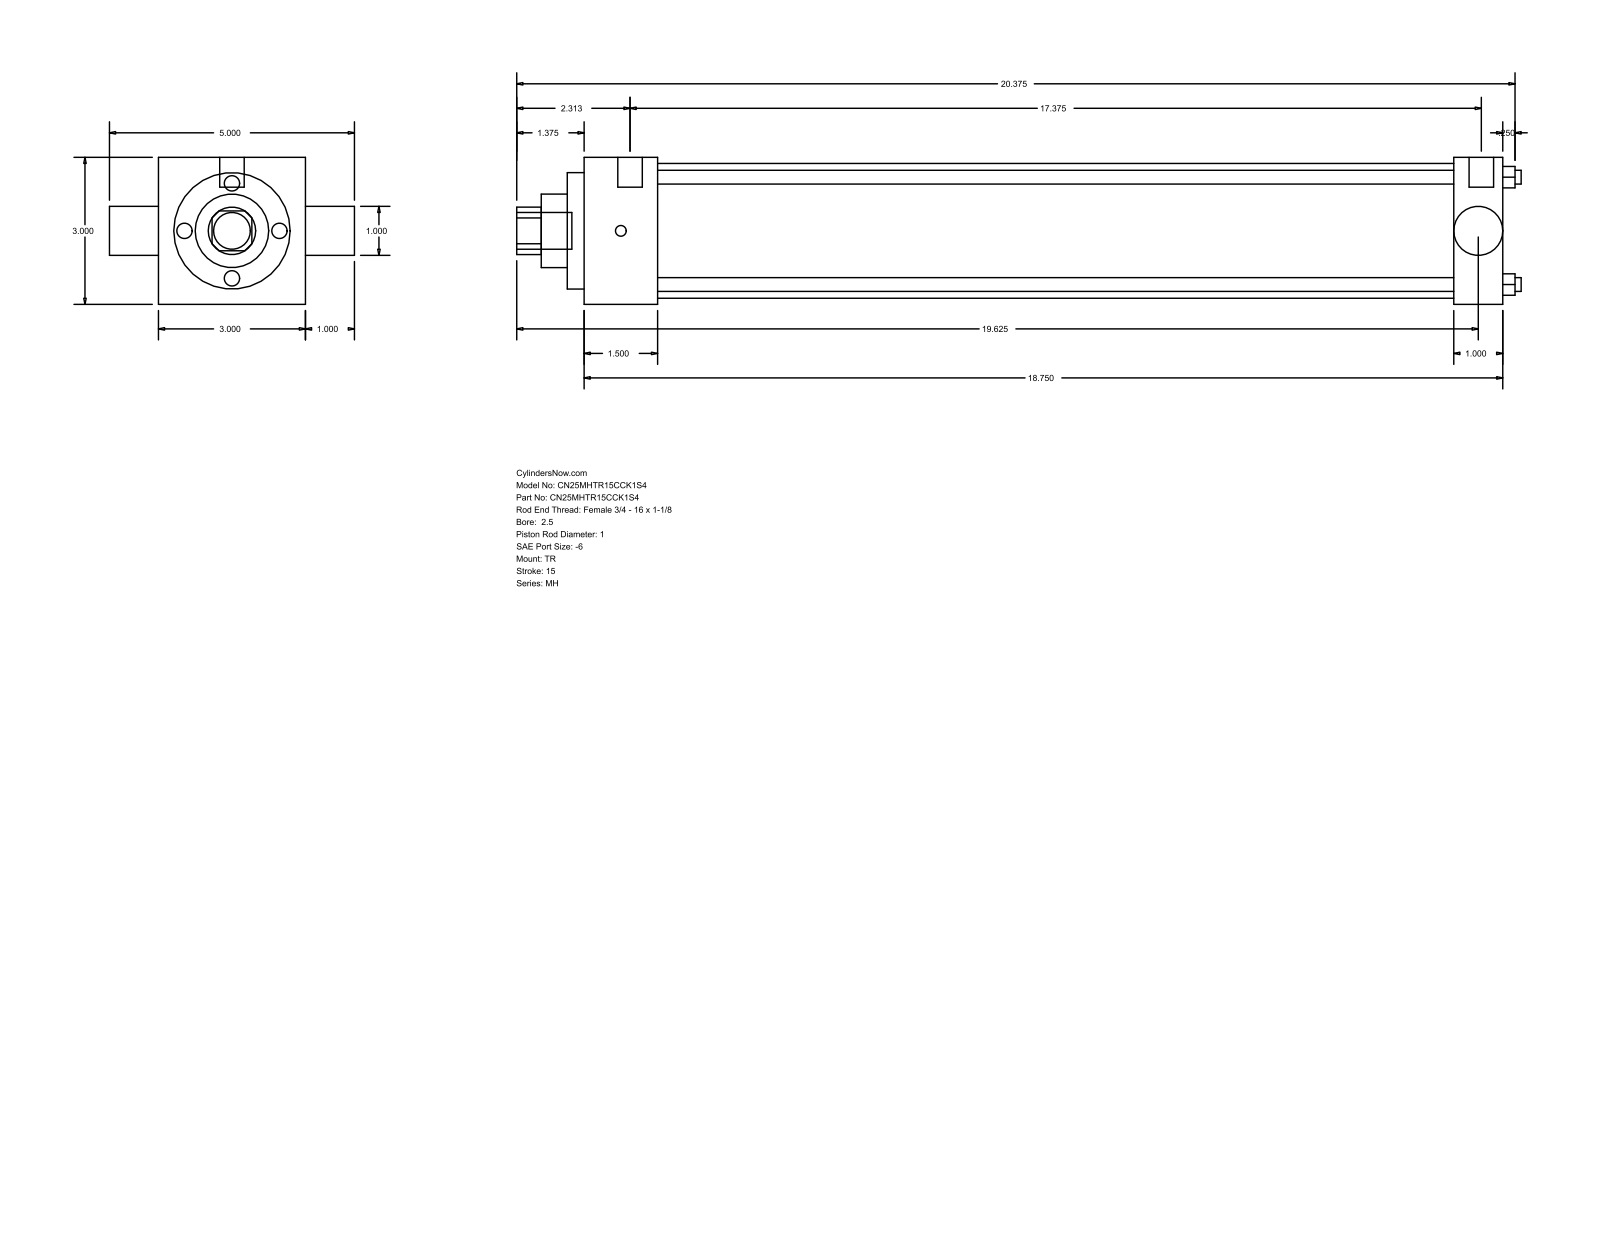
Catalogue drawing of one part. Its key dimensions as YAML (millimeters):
part_name: "MH_TR__0250_1"
step_written_by: "GSSL Pune (CONFIG_CONTROL_DESIGN)"
units: millimeters
bodies: {solids: 0, faces: 86, planar: 61, cylindrical: 25, other: 0}
overall_size: [520.7, 127, 76.2]
round_holes:
  - {diameter: 7.14, count: 4}
  - {diameter: 25.35, count: 1}
  - {diameter: 25.4, count: 1}
  - {diameter: 38.1, count: 1}
  - {diameter: 60.33, count: 1}
  - {diameter: 69.85, count: 1}
round_bosses_or_shafts:
  - {diameter: 5.56, count: 3}
  - {diameter: 12.7, count: 2}
  - {diameter: 19.05, count: 1}
partial_cylinders:
  - {radius: 12.29, count: 1}
face_to_face_distances: [76.2, 476.26, 38.11, 438.15, 450.85, 412.74, 25.41, 8.73, 46.84, 459.58]
hole_center_spacings: [39.33, 55.62, 78.66]
